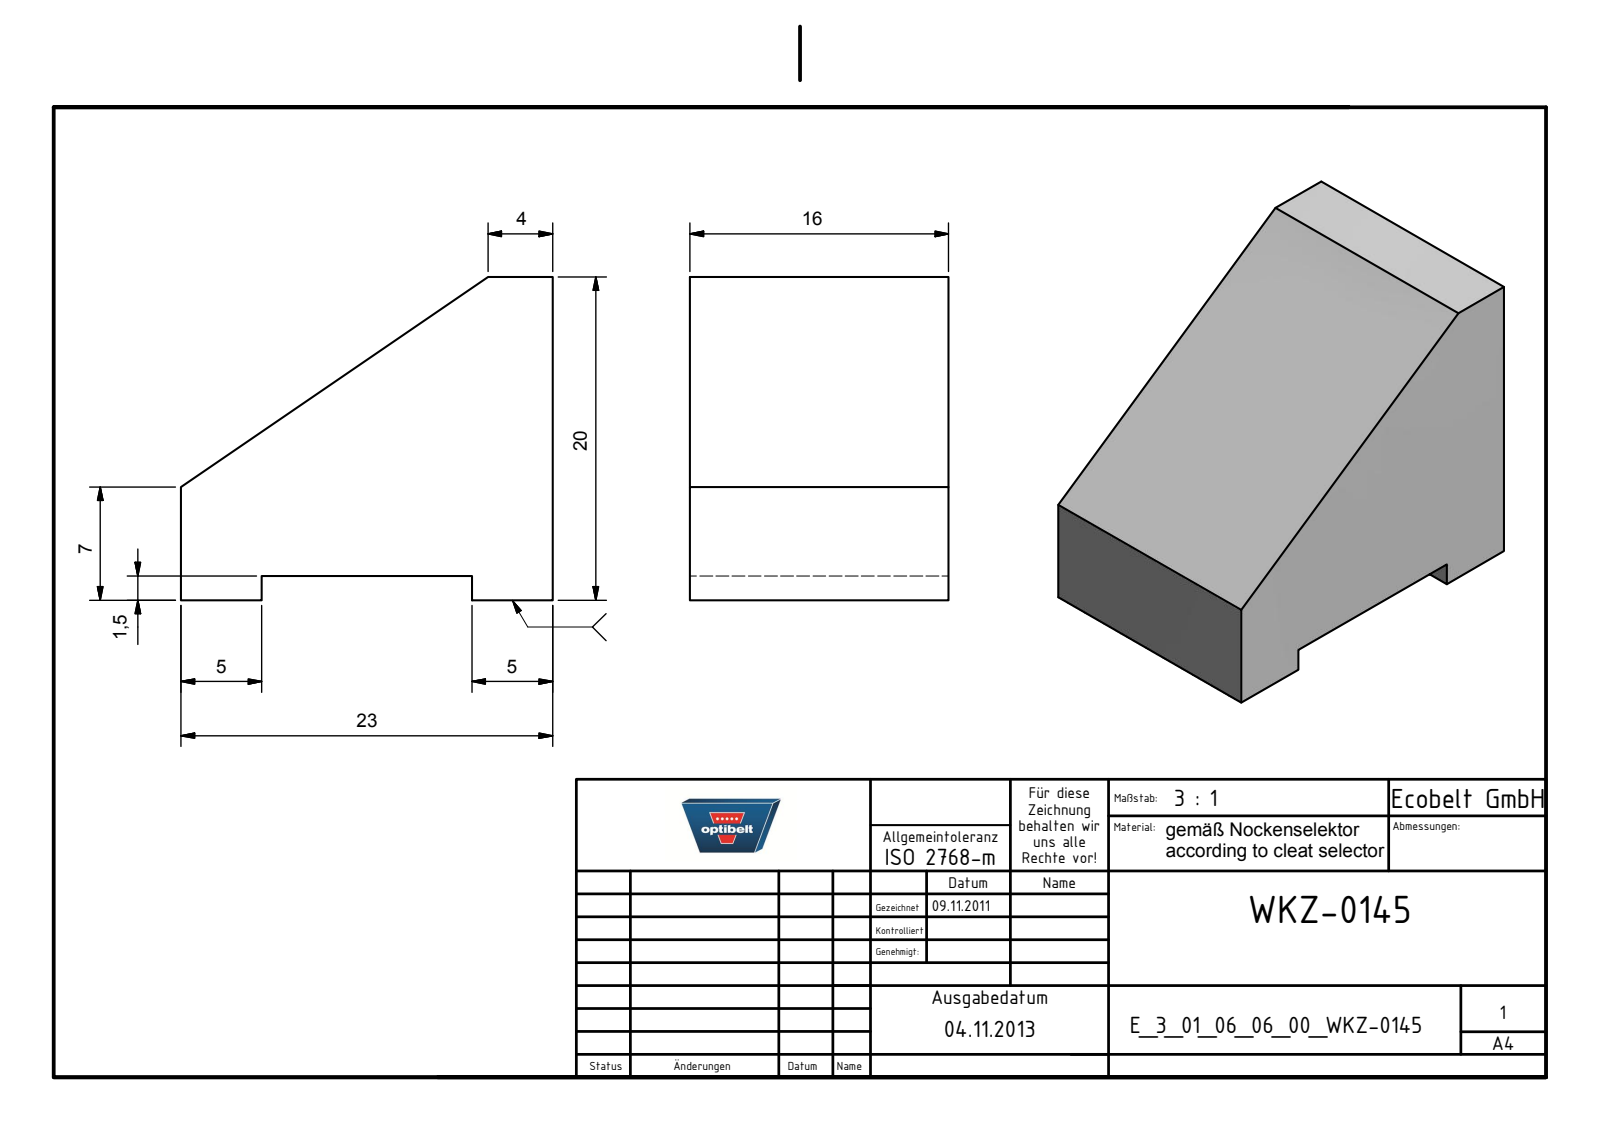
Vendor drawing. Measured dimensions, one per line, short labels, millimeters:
name: E_3_01_06_06_00_WKZ-0145
written by: Autodesk Inventor 2025 (AUTOMOTIVE_DESIGN)
unit: mm
bodies: 1 solid, 11 faces (11 planar, 0 cylindrical, 0 other)
size: 23 × 20 × 16
volume: 5 072 mm³; area: 1 914 mm²
face distances: 16, 1.5, 23, 20, 18.5, 5, 18, 13
